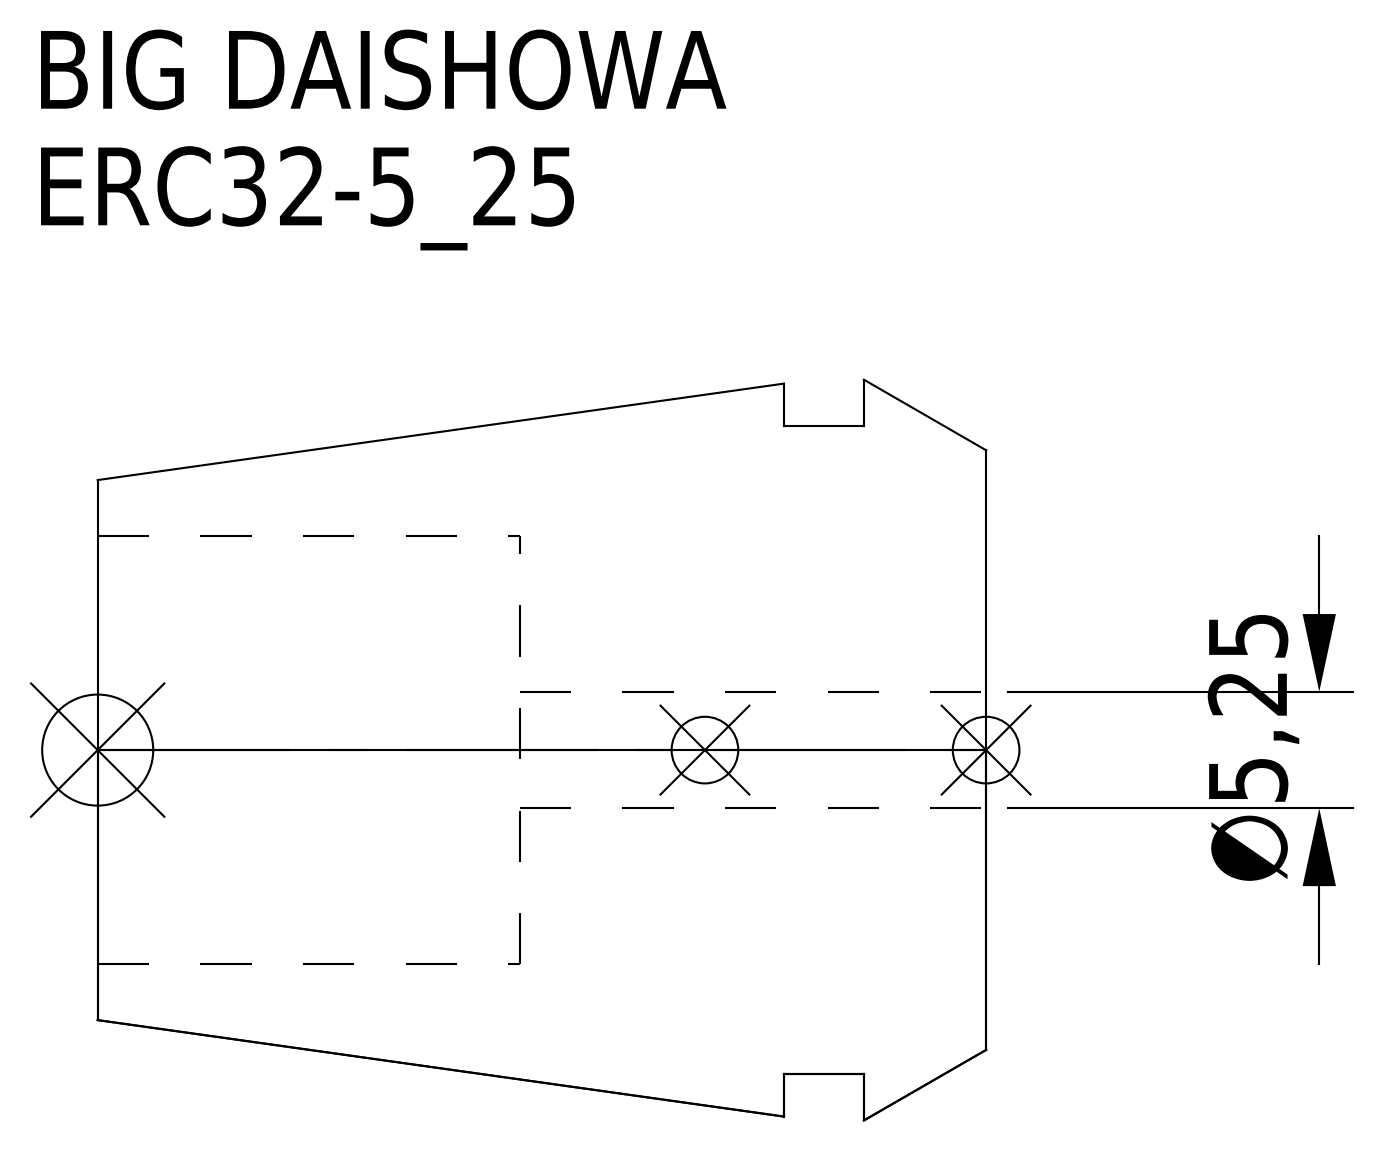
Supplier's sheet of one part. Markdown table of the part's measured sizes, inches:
| quantity | value |
| --- | --- |
| part name | ERC32-5_25 |
| STEP written by | CREO PARAMETRIC BY PTC INC, 2016380 (AUTOMOTIVE_DESIGN) |
| units | inches |
| bodies | 1 solid, 15 faces (5 planar, 6 cylindrical, 4 other) |
| overall size | 1.575 × 1.313 × 1.313 |
| volume | 1.247 in³ |
| surface area | 10.27 in² |
| round holes (diameter × count) | 0.207 × 1, 0.76 × 1 |
| round bosses / shafts (diameter × count) | 1.15 × 1 |
| main face-to-face distances | 0.827, 0.217, 0.61, 0.358, 0.142, 0.469, 1.575, 1.358, 1.217, 0.748 |
